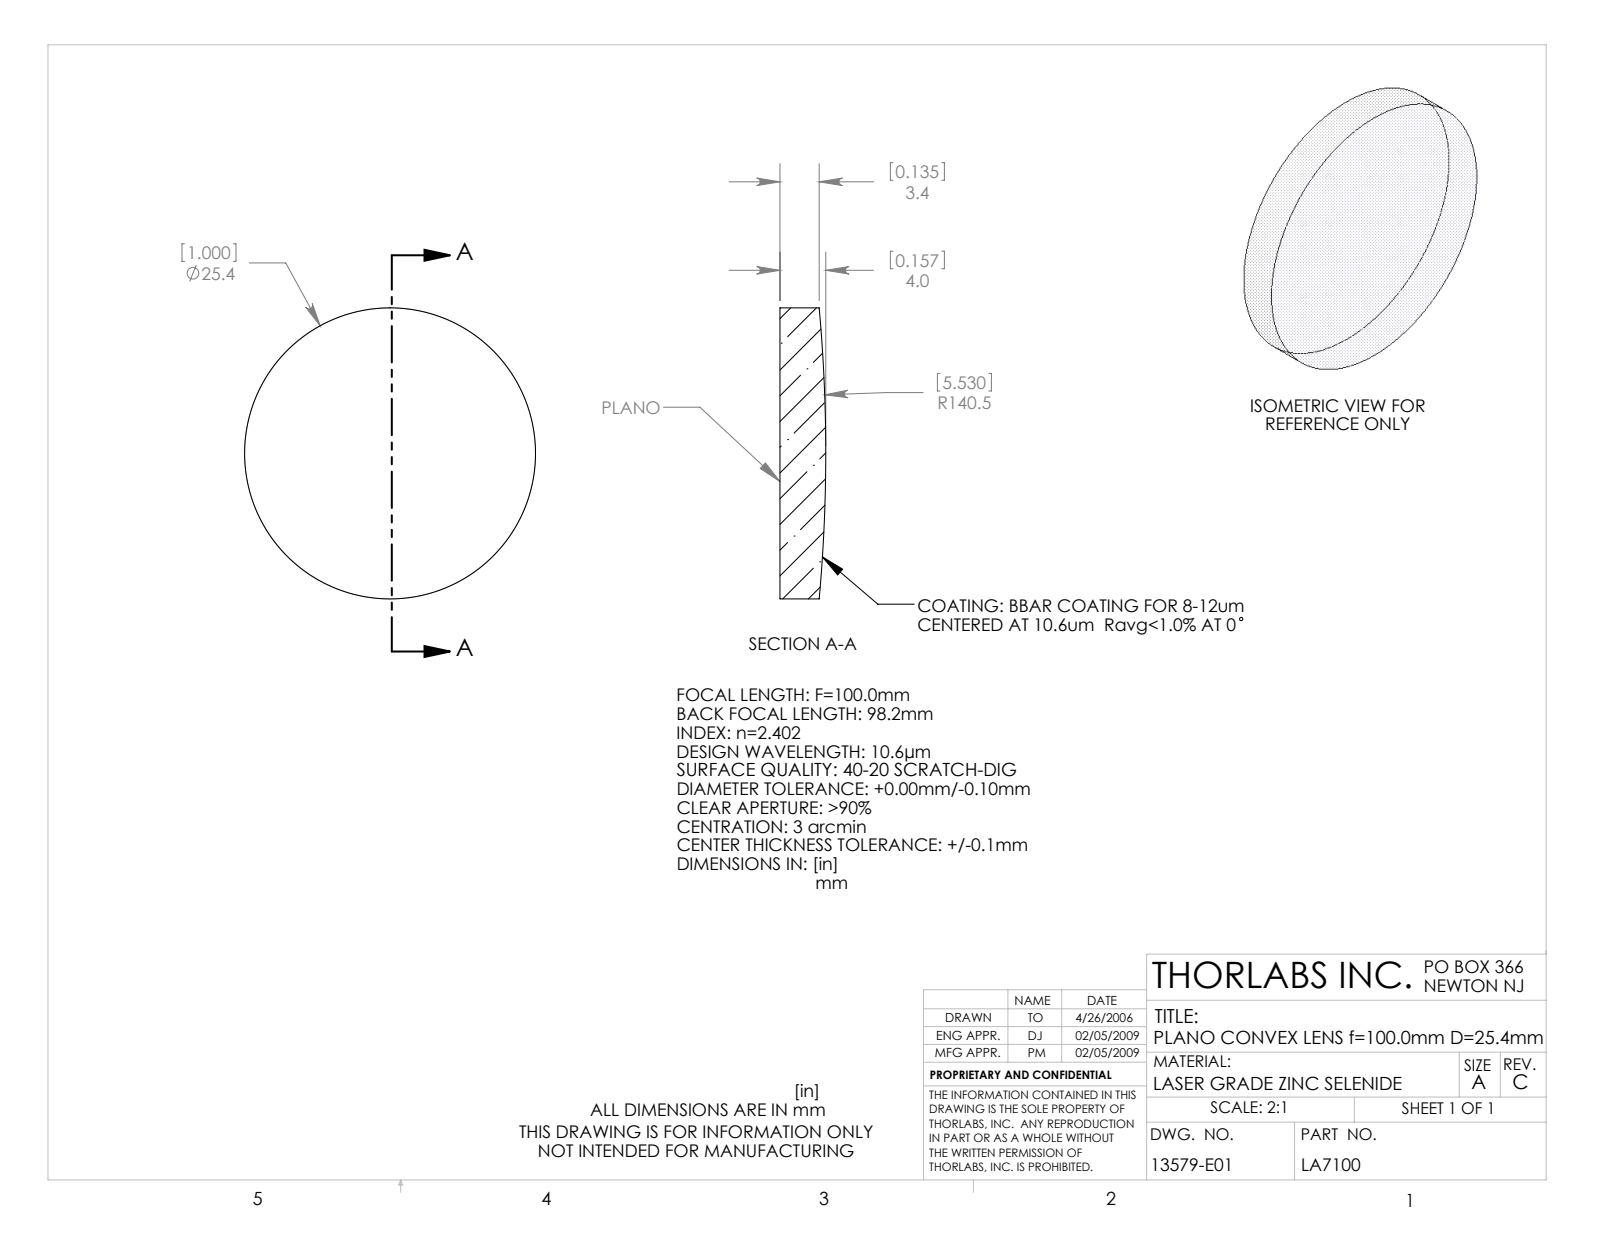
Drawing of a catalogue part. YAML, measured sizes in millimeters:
part_name: "13579-E0W"
step_written_by: "SolidWorks 2007 (AUTOMOTIVE_DESIGN)"
units: millimeters
bodies: {solids: 0, faces: 5, planar: 1, cylindrical: 2, other: 2}
overall_size: [25.4, 25.4, 4]
round_bosses_or_shafts:
  - {diameter: 25.4, count: 1}
